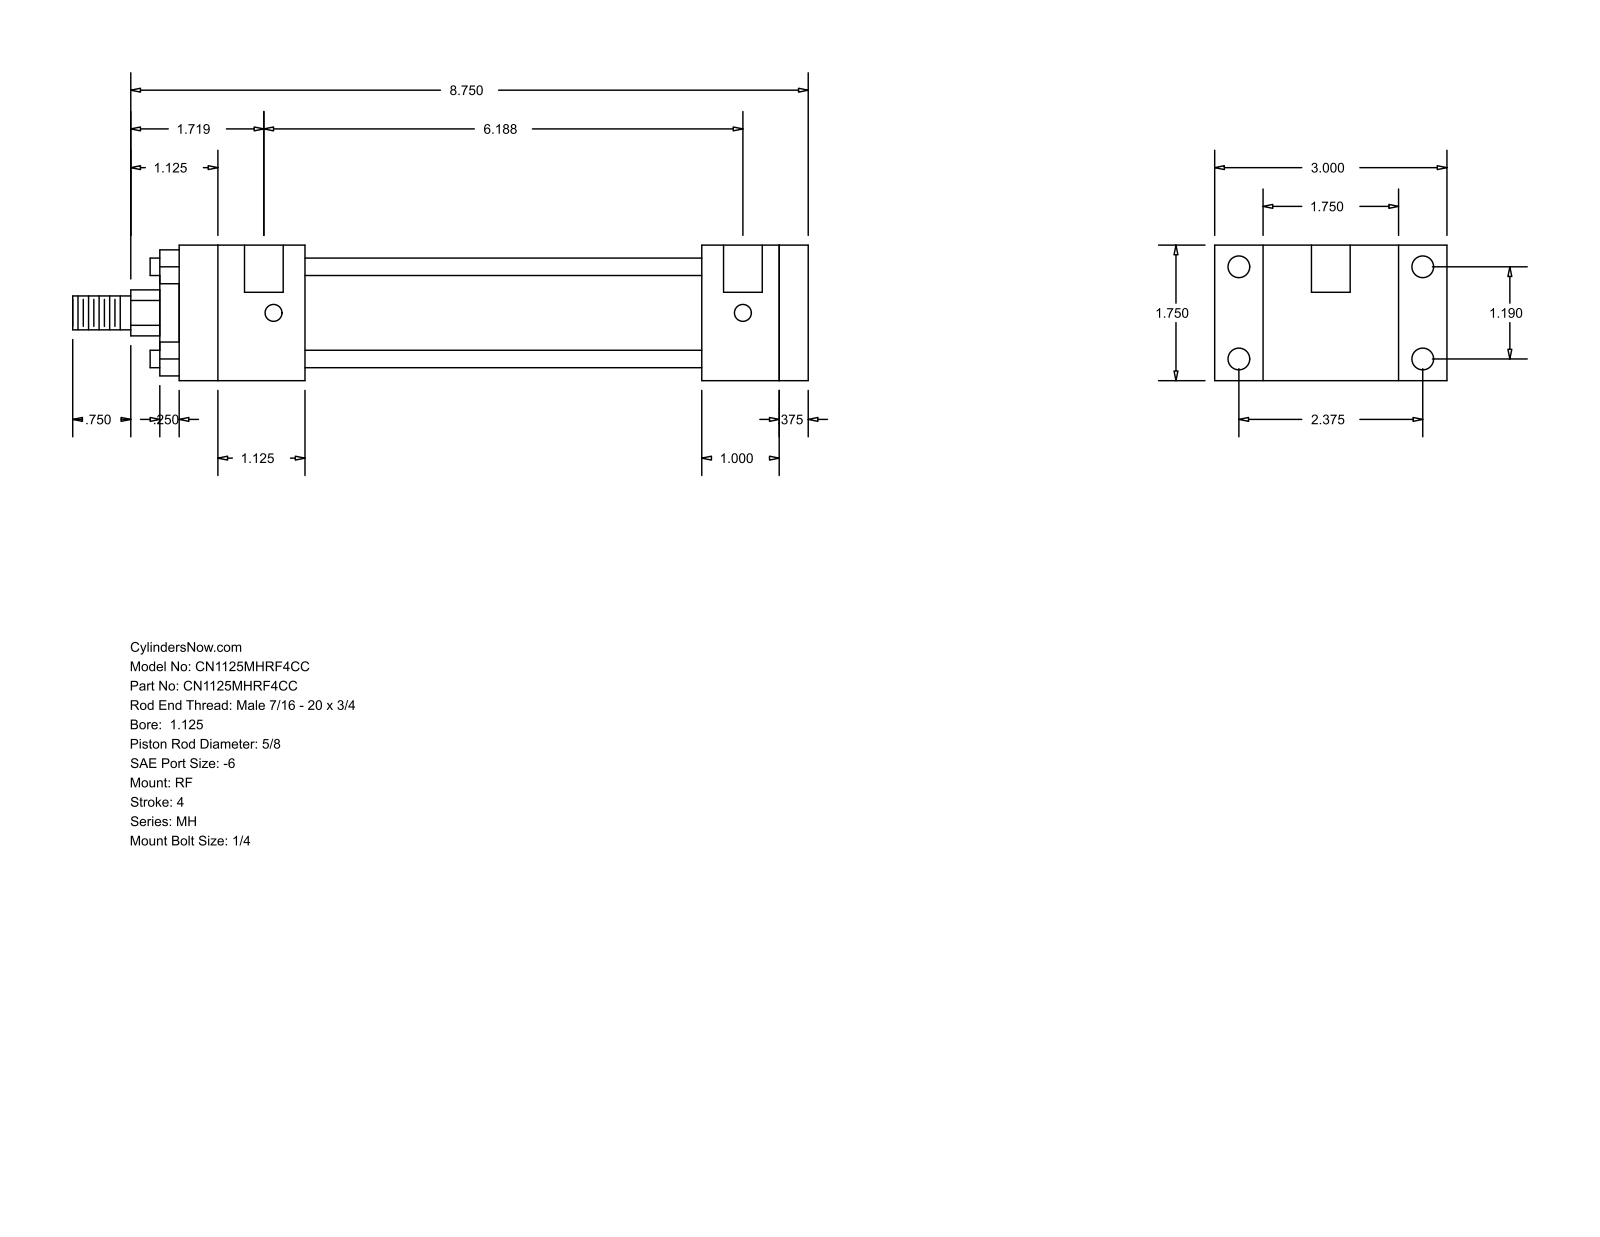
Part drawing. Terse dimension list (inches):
name: MH_RF__0112_0.625
written by: GSSL Pune (CONFIG_CONTROL_DESIGN)
unit: in
bodies: 0 solids, 92 faces (64 planar, 28 cylindrical, 0 other)
size: 9.5 × 3 × 1.75
holes: 4× ⌀0.219, 4× ⌀0.281, 2× ⌀0.5
bosses: 4× ⌀0.225, 1× ⌀1.375, 1× ⌀1.125, 1× ⌀0.625, 1× ⌀0.437
rounds: 1× R0.297
face distances: 1.75, 0.375, 8.125, 1, 1.375, 0.625, 6.125, 6.5, 5.125, 1.625
hole spacings: 1.19, 2.375, 2.656, 6.063, 0.125, 6.187
